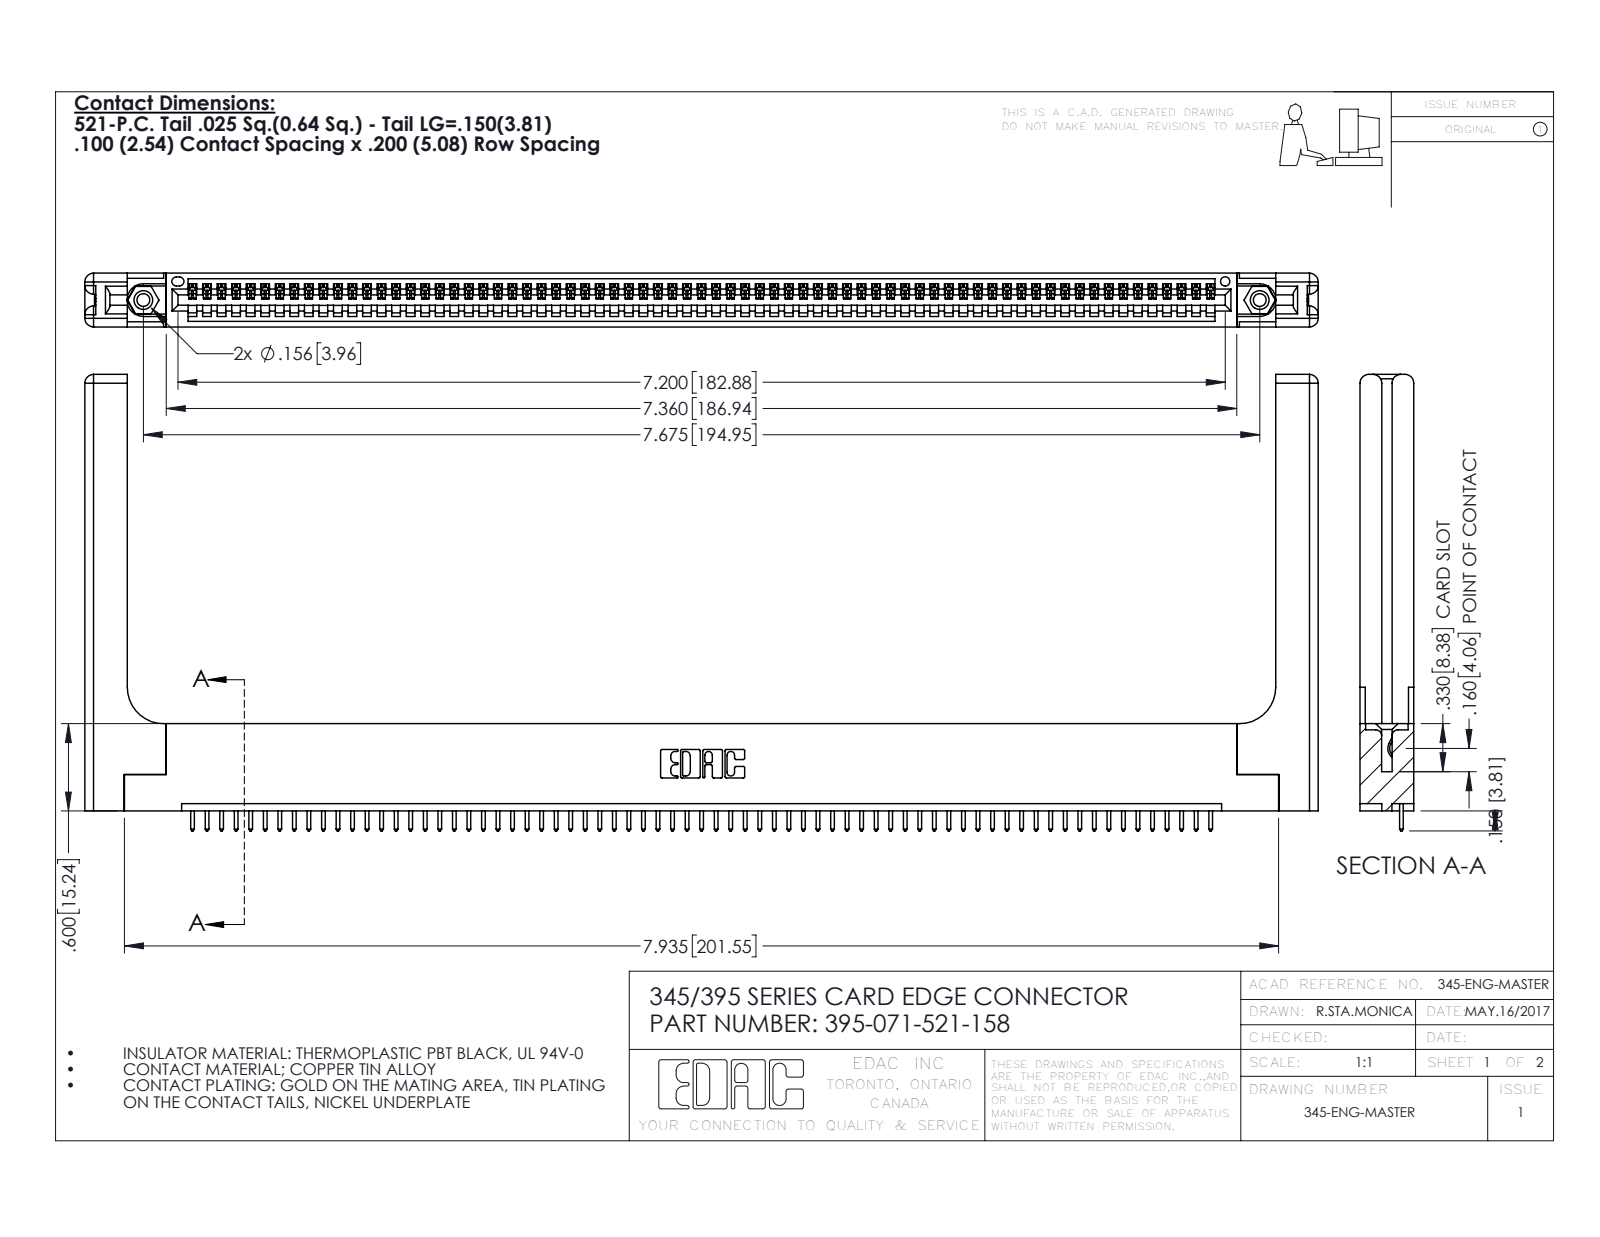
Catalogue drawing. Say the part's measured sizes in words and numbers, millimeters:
The part is named "345-220-058_345-220-058; 395-071-521-158; 345-250-001_345-250-001-102; 345-292-001_345-293-121 (+1 more)". Its 3-D file was written by "SolidWorks 2016 (CONFIG_CONTROL_DESIGN)". It is 76 solids with 4500 faces: 3068 planar, 1372 cylindrical and 60 other. Overall it measures 215.4 by 79.7 by 9.4 millimeters. Its volume is 28 990 cubic millimeters and its surface area 32 140 square millimeters. Round holes: 2 of diameter 2.3, 2 of diameter 3.2, 2 of diameter 4, 1 of diameter 1.6. Round bosses or shafts: 2 of diameter 3.9. Partial cylindrical surfaces (rounded edges, fillets, slot ends): 142 of radius 0.2, 142 of radius 0.3, 22 of radius 0.3, 16 of radius 1.5, 6 of radius 0.2, 6 of radius 0.8, 3 of radius 0.7, 2 of radius 0.8. The main face-to-face distances are 1.8, 7.6, 9.4, 5.1, 2.5, 6.9, 0.6, 5.7, 3.8, 3.8. The hole center spacings are 6.9, 189, 194.9.
